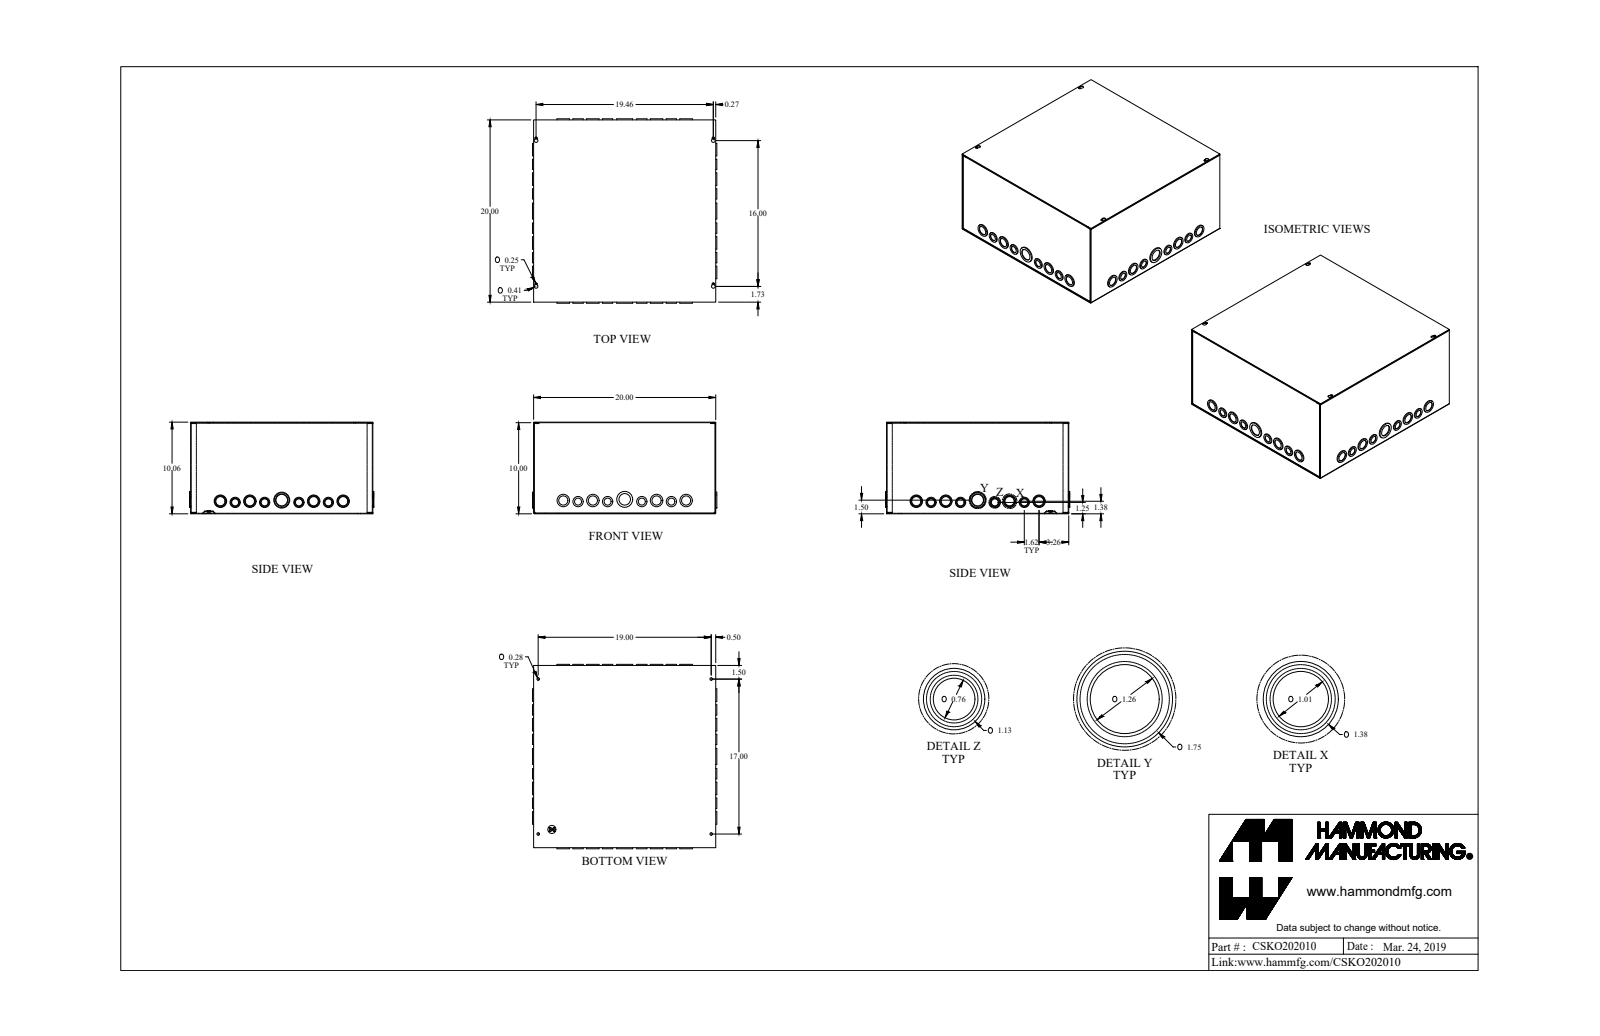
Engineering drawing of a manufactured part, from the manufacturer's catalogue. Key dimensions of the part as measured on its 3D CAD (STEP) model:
Part name (STEP PRODUCT): CSKO202010_Default
STEP written by: SolidWorks 2019 (CONFIG_CONTROL_DESIGN)
Units: inches
Bodies: 4 solids, 637 faces (269 planar, 360 cylindrical, 8 other)
Overall size (bounding box): 20.234 × 20.234 × 10.057
Volume: 96.25 in³ · Surface area: 3 397 in²
Round holes (diameter × count): ⌀1.011 ×16, ⌀1.261 ×10, ⌀0.761 ×8, ⌀0.17 ×5, ⌀0.281 ×4, ⌀1.636 ×2, ⌀0.5 ×1
Round bosses / shafts (diameter × count): ⌀1.125 ×14, ⌀1.375 ×9, ⌀0.875 ×8, ⌀1.125 ×4, ⌀0.875 ×4, ⌀1.75 ×2, ⌀1.375 ×1, ⌀0.492 ×1
Partial cylindrical surfaces — rounded edges, fillets, slot ends (radius × count): R0.029 ×12, R0.086 ×12, R0.057 ×8, R0.125 ×4, R0.203 ×4
Main face-to-face distances: 0.057, 10, 19.943, 9.943, 20, 10.057, 19.886, 0.114, 0.08, 9.863
Hole centre spacings: 1.625, 3.24, 8.621, 7, 10.24, 0.55, 1.896, 3.502
